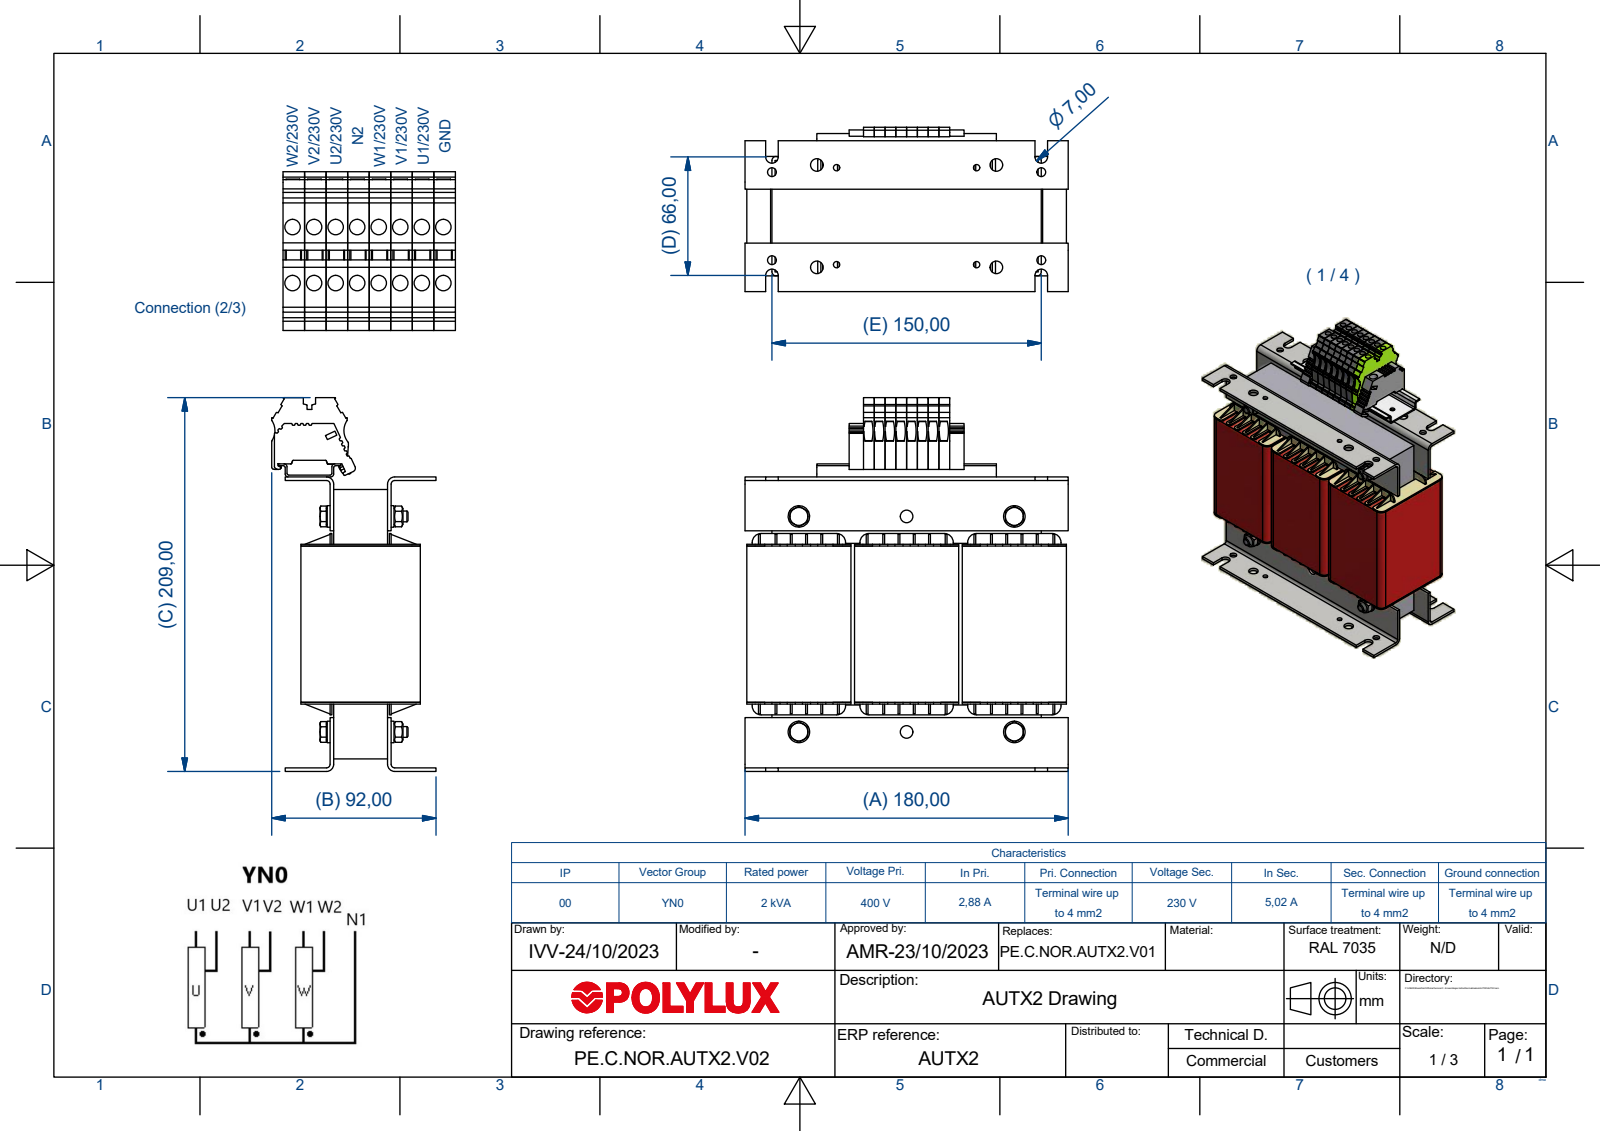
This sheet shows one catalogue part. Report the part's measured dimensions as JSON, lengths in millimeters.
{"part_name": "AUTX2; Núcleo RC30x30; CAR0002T (30x30); BRI30-3IP02 (+8 more)", "step_written_by": "Autodesk Inventor 2018 (AUTOMOTIVE_DESIGN)", "units": "millimeters", "bodies": {"solids": 38, "faces": 2506, "planar": 1728, "cylindrical": 734, "other": 44}, "overall_size": [208.15, 180, 87.5], "volume_mm3": 1428000, "surface_area_mm2": 434248, "round_holes": [[4.3, 16], [7, 10], [4.92, 8], [3.5, 6], [6, 4], [6.4, 4], [3, 2], [5.8, 2]], "round_bosses_or_shafts": [[12, 4], [8.9, 4]], "partial_cylinders_radius": [[0.5, 33], [2.25, 24], [24.01, 16], [0.1, 13], [0.3, 12], [1, 12], [4.65, 12], [5, 12]], "face_to_face_distances": [2, 60, 1, 32, 46, 1.25, 2.25, 32.25, 30, 120], "hole_center_spacings": [6, 16.71, 12, 19.68, 18, 23.82, 15.6, 24]}
